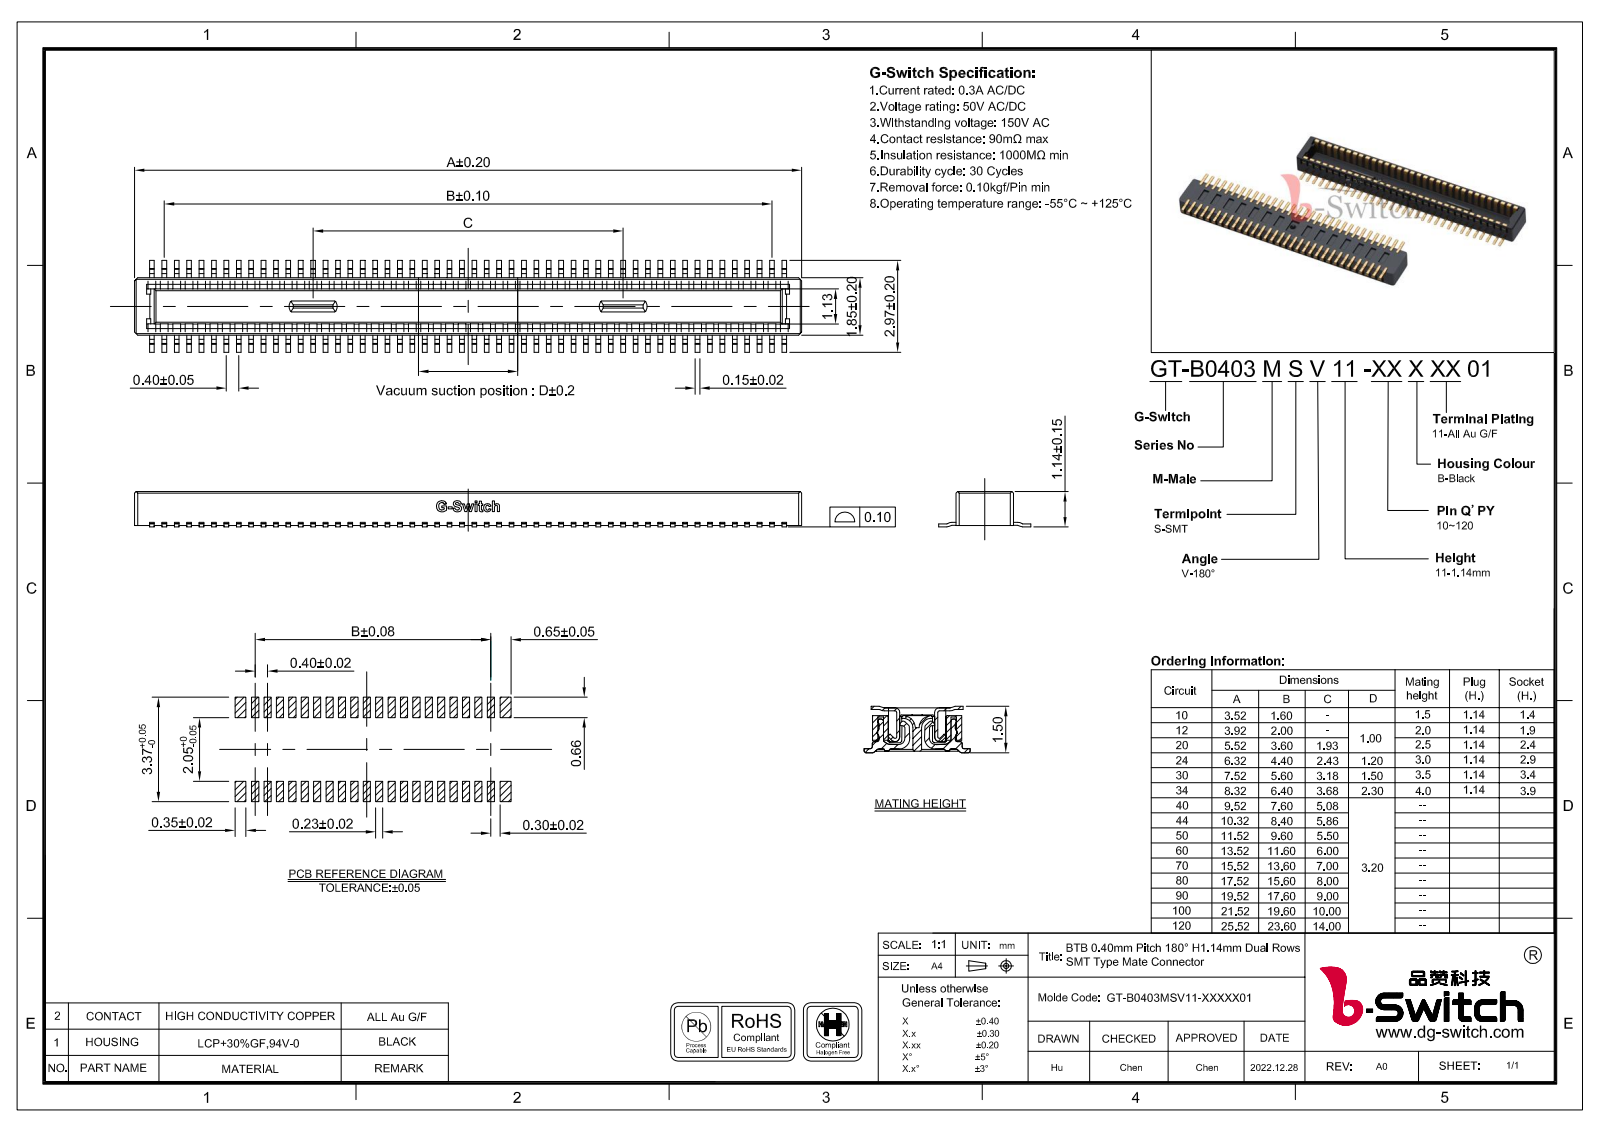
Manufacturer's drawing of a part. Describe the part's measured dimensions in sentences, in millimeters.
The part is named "GT-B0403MSV11-XXXXX01". Its 3-D file was written by "PRO/ENGINEER BY PARAMETRIC TECHNOLOGY CORPORATION, 2015070 (CONFIG_CONTROL_DESIGN)". It is 1 solid with 737 faces: 455 planar, 196 cylindrical and 86 other. Overall it measures 7.52 by 2.97 by 1.15 millimeters. Its volume is 9 cubic millimeters and its surface area 71 square millimeters. Partial cylindrical surfaces (rounded edges, fillets, slot ends): 12 of radius 0.15, 4 of radius 0.3, 2 of radius 0.25. The main face-to-face distances are 1.48, 0.36, 1.84, 1.09, 1.12, 0.86, 1.1, 0.39, 7.52, 1.05.
